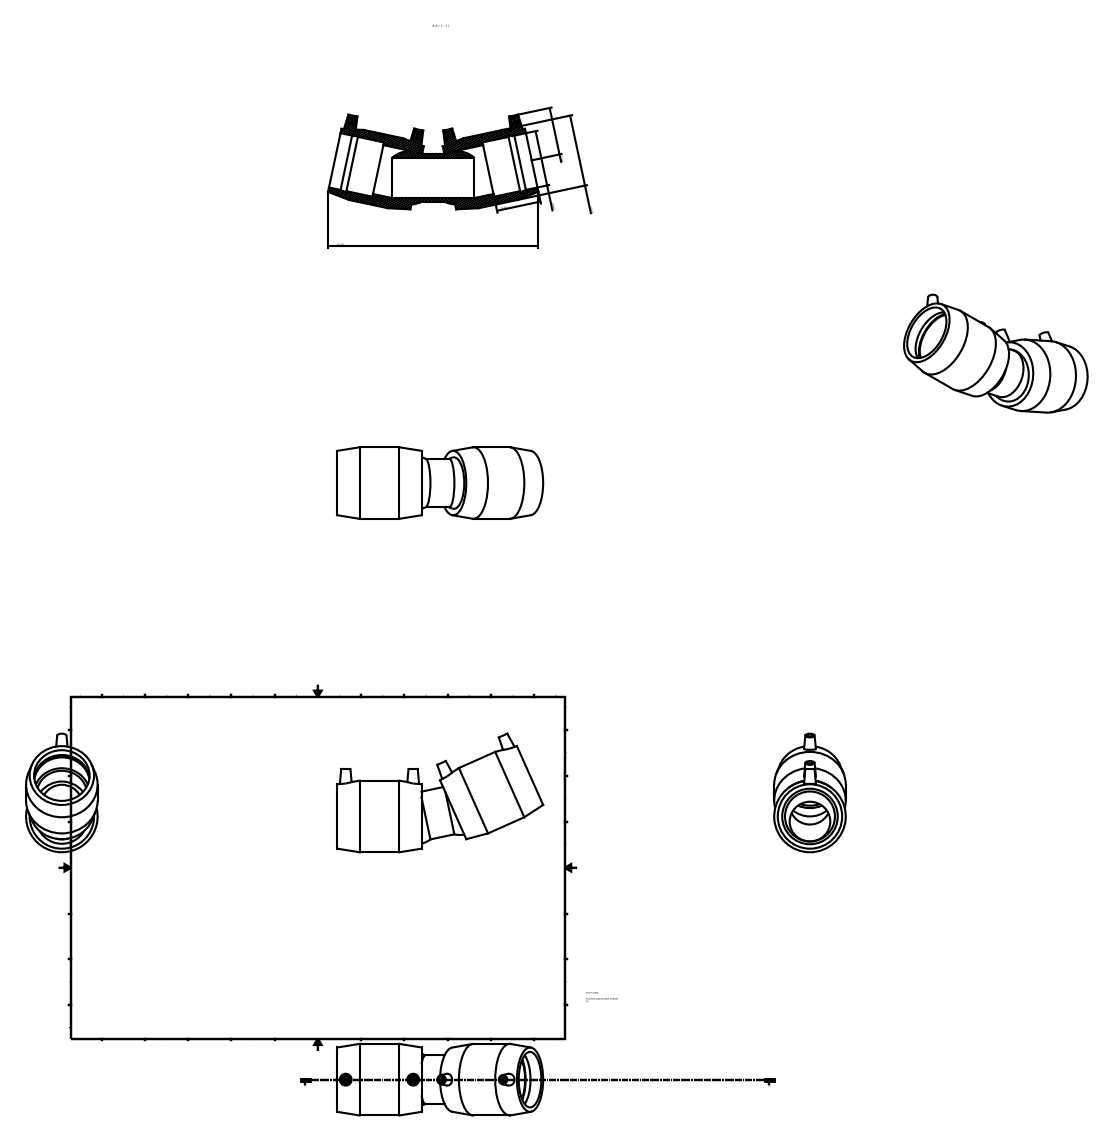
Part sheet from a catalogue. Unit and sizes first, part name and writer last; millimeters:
Units: millimetres
Overall size (bounding box): 333.55 × 192.23 × 116
Round holes (diameter × count): ⌀10 ×4, ⌀90 ×3, ⌀81 ×2, ⌀65.84 ×1
Round bosses / shafts (diameter × count): ⌀4 ×4, ⌀116 ×2, ⌀78.72 ×1
Main face-to-face distances: 136.4, 136.47, 72, 64.4, 64.44, 72.03, 28.8, 43.2, 107.6, 107.66
Hole centre spacings: 109.12
Volume: 1 366 000 mm³ · Surface area: 228 249 mm²
Bodies: 1 solid, 54 faces (20 planar, 20 cylindrical, 14 other)
Part name (STEP PRODUCT): 4947C4090
STEP written by: Autodesk Inventor 2015 (AUTOMOTIVE_DESIGN)
